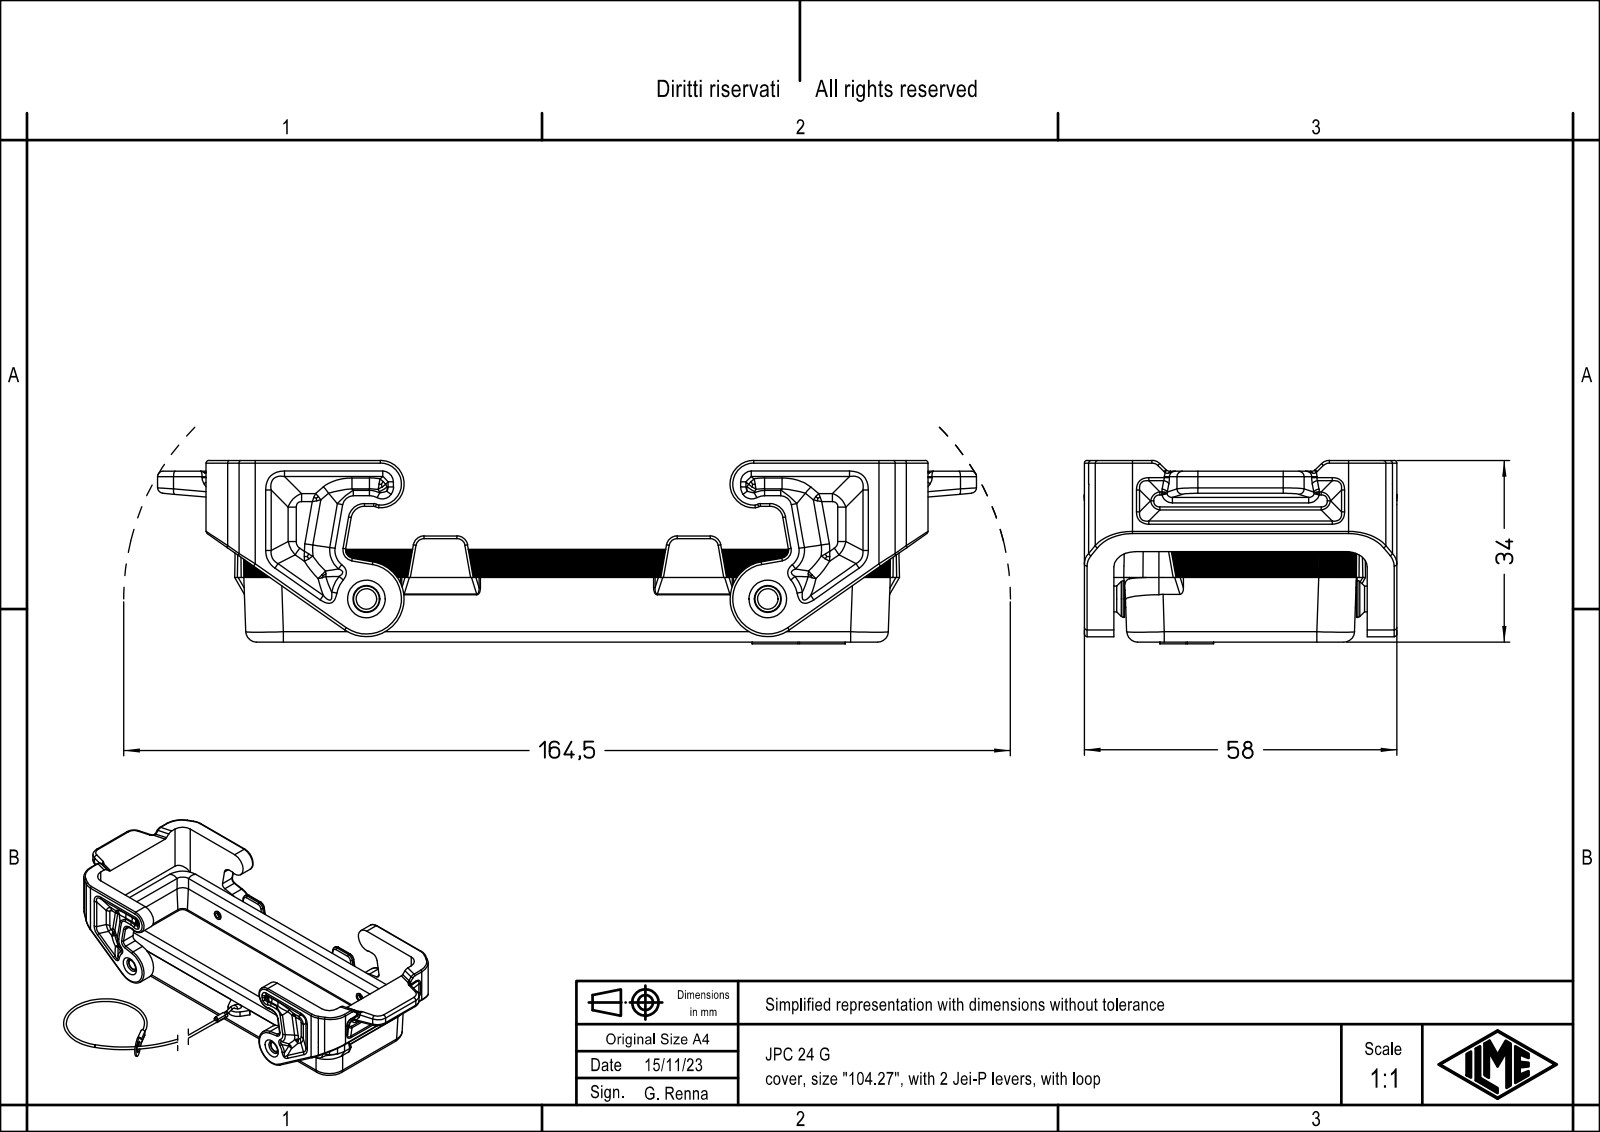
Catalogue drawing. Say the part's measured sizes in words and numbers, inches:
The part is named "JPC 24 G". Its 3-D file was written by "Creo Elements/Direct Modeling 20.1B 02-Apr-2019 (C) Parametric Technology GmbH (AUTOMOTIVE_DESIGN)". It is 1 solid with 857 faces: 191 planar, 274 cylindrical and 392 other. Overall it measures 5.984 by 2.287 by 1.339 inches. Its volume is 3.276 cubic inches and its surface area 51.38 square inches. Round holes: 2 of diameter 0.189, 1 of diameter 0.118. Round bosses or shafts: 2 of diameter 0.268. Partial cylindrical surfaces (rounded edges, fillets, slot ends): 47 of radius 0.02, 34 of radius 0.039, 31 of radius 0.079, 26 of radius 0.118, 15 of radius 0.013, 12 of radius 0.059, 12 of radius 0.236, 10 of radius 0.276. The main face-to-face distances are 0.098, 1.85, 0.157, 0.217, 2.067, 0.238, 1.77, 1.531, 0.455, 1.829. The hole center spacings are 2.933.
